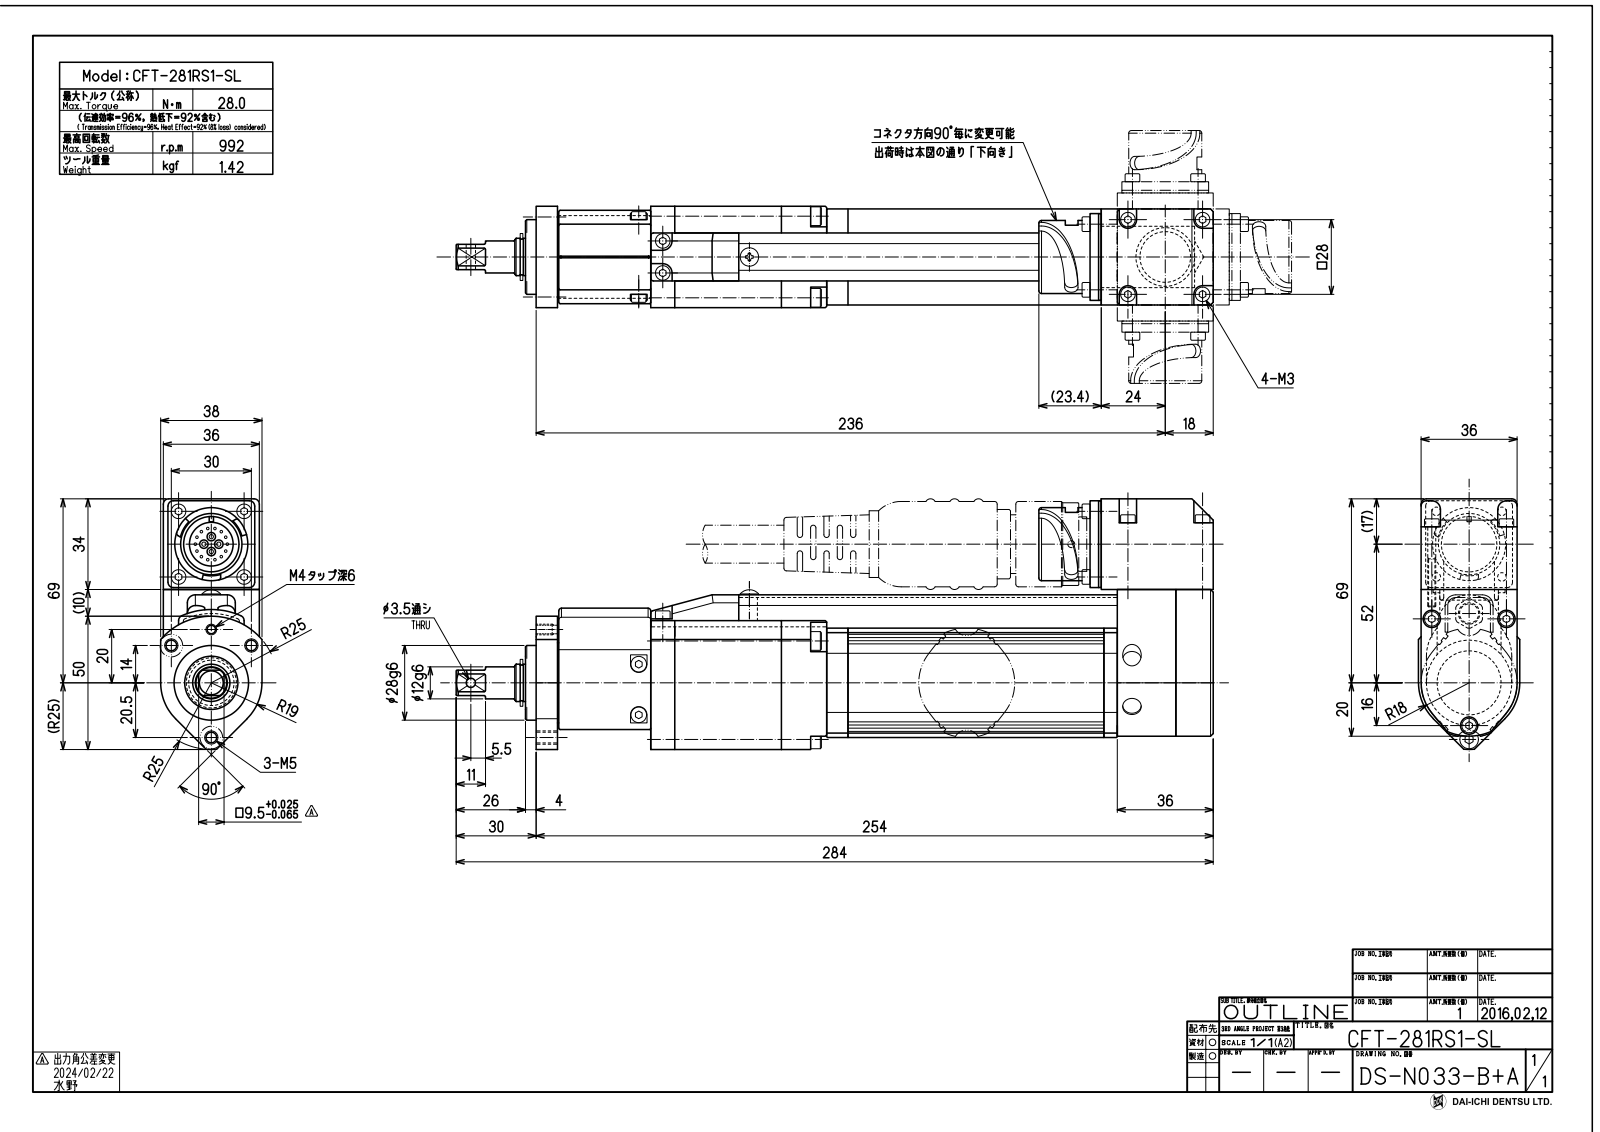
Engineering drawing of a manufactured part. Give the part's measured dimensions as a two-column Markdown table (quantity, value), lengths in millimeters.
| quantity | value |
| --- | --- |
| part name | CFT-281RS1-SL |
| STEP written by | SolidWorks 2015 (CONFIG_CONTROL_DESIGN) |
| units | millimeters |
| bodies | 30 solids, 434 faces (213 planar, 142 cylindrical, 79 other) |
| overall size | 284 × 94 × 38 |
| volume | 427 577 mm³ |
| surface area | 94 839 mm² |
| round holes (diameter × count) | 4.2 × 3, 3.3 × 1, 3.5 × 1, 20.4 × 1 |
| round bosses / shafts (diameter × count) | 5.5 × 10, 7 × 4, 28 × 1, 27.4 × 1, 17.6 × 1, 14 × 1, 13.4 × 1, 12 × 1 |
| partial cylindrical surfaces (radius × count) | 3 × 6, 1 × 5, 0.5 × 4, 3.25 × 4, 20.5 × 4, 5 × 3, 2 × 2, 3.5 × 2 |
| main face-to-face distances | 36, 18, 9, 1, 109, 40, 162, 23, 27, 121 |
| hole center spacings | 16.16, 37.62, 40.85, 30, 32, 40.5, 72.5 |
